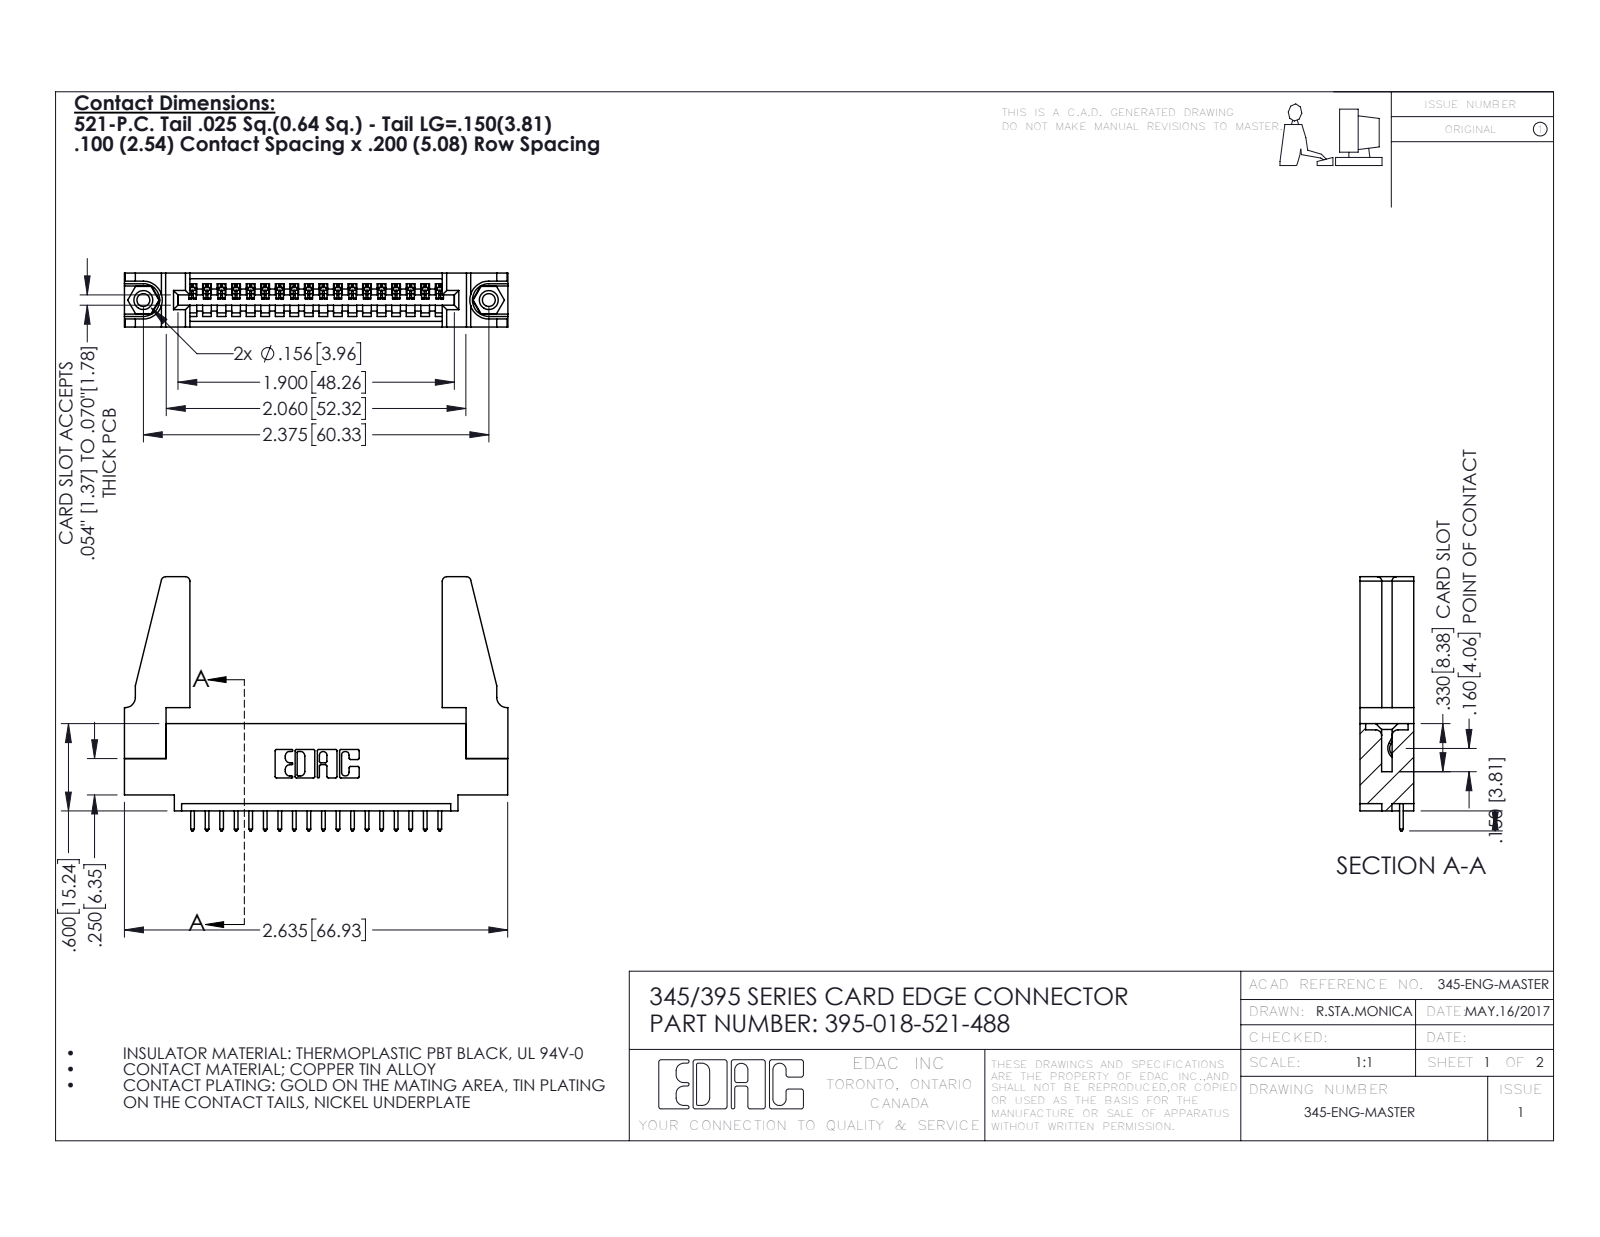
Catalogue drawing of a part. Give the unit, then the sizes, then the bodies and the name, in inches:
Units: inches
Overall size (bounding box): 2.636 × 1.747 × 0.37
Round holes (diameter × count): ⌀0.089 ×2, ⌀0.125 ×2, ⌀0.156 ×2, ⌀0.064 ×1
Round bosses / shafts (diameter × count): ⌀0.155 ×2
Partial cylindrical surfaces — rounded edges, fillets, slot ends (radius × count): R0.006 ×36, R0.01 ×36, R0.01 ×22, R0.03 ×8, R0.007 ×6, R0.031 ×6, R0.026 ×3, R0.031 ×2
Main face-to-face distances: 0.37, 0.072, 0.298, 0.2, 0.098, 0.272, 0.025, 0.225, 0.15, 0.148
Hole centre spacings: 0.27, 2.141, 2.375
Volume: 0.567 in³ · Surface area: 16.6 in²
Bodies: 23 solids, 1298 faces (876 planar, 406 cylindrical, 16 other)
Part name (STEP PRODUCT): 345-220-078_345-220-088; 345-292-001_345-293-121; 345 Part_0.110 Offset - 0.156 Dia-TH; 395-018-521-488 (+1 more)
STEP written by: SolidWorks 2016 (CONFIG_CONTROL_DESIGN)
